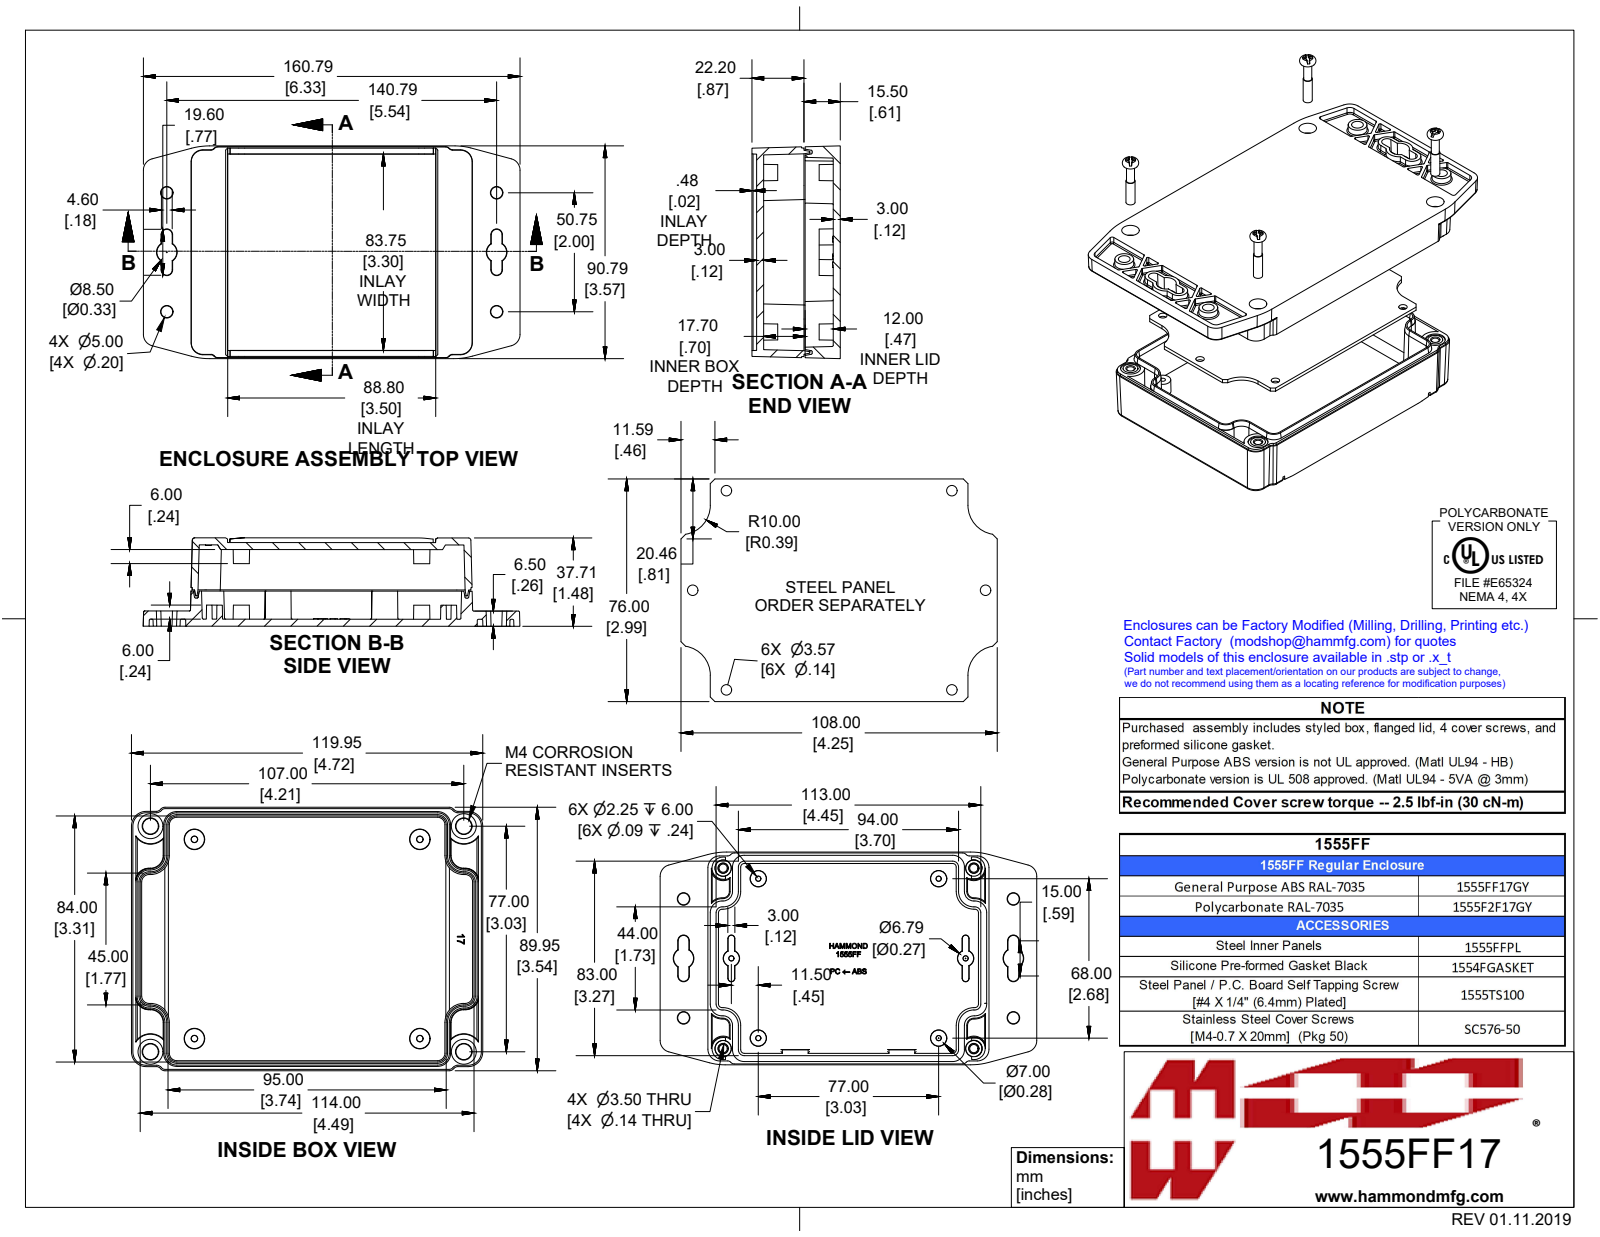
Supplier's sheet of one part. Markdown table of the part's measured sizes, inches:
| quantity | value |
| --- | --- |
| part name | 1555FF17GY |
| STEP written by | SolidWorks 2019 (CONFIG_CONTROL_DESIGN) |
| units | inches |
| bodies | 11 solids, 1377 faces (638 planar, 261 cylindrical, 478 other) |
| overall size | 6.33 × 3.574 × 1.484 |
| volume | 9.069 in³ |
| surface area | 170.3 in² |
| round holes (diameter × count) | 0.118 × 6, 0.128 × 4, 0.138 × 4, 0.335 × 4 |
| round bosses / shafts (diameter × count) | 0.25 × 4, 0.218 × 4, 0.21 × 4, 0.153 × 4, 0.135 × 4 |
| partial cylindrical surfaces (radius × count) | 0.02 × 127, 0.197 × 12, 0.039 × 6, 0.089 × 4, 0.138 × 4, 0.187 × 4, 0.394 × 4, 0.976 × 1 |
| main face-to-face distances | 0.118, 1.287, 0.236, 0.354, 0.933, 1.169, 1.406, 1.051, 0.419, 0.3 |
| hole center spacings | 0.617, 1.413, 1.522, 2.915, 3.031, 3.626, 3.733, 4.348 |
